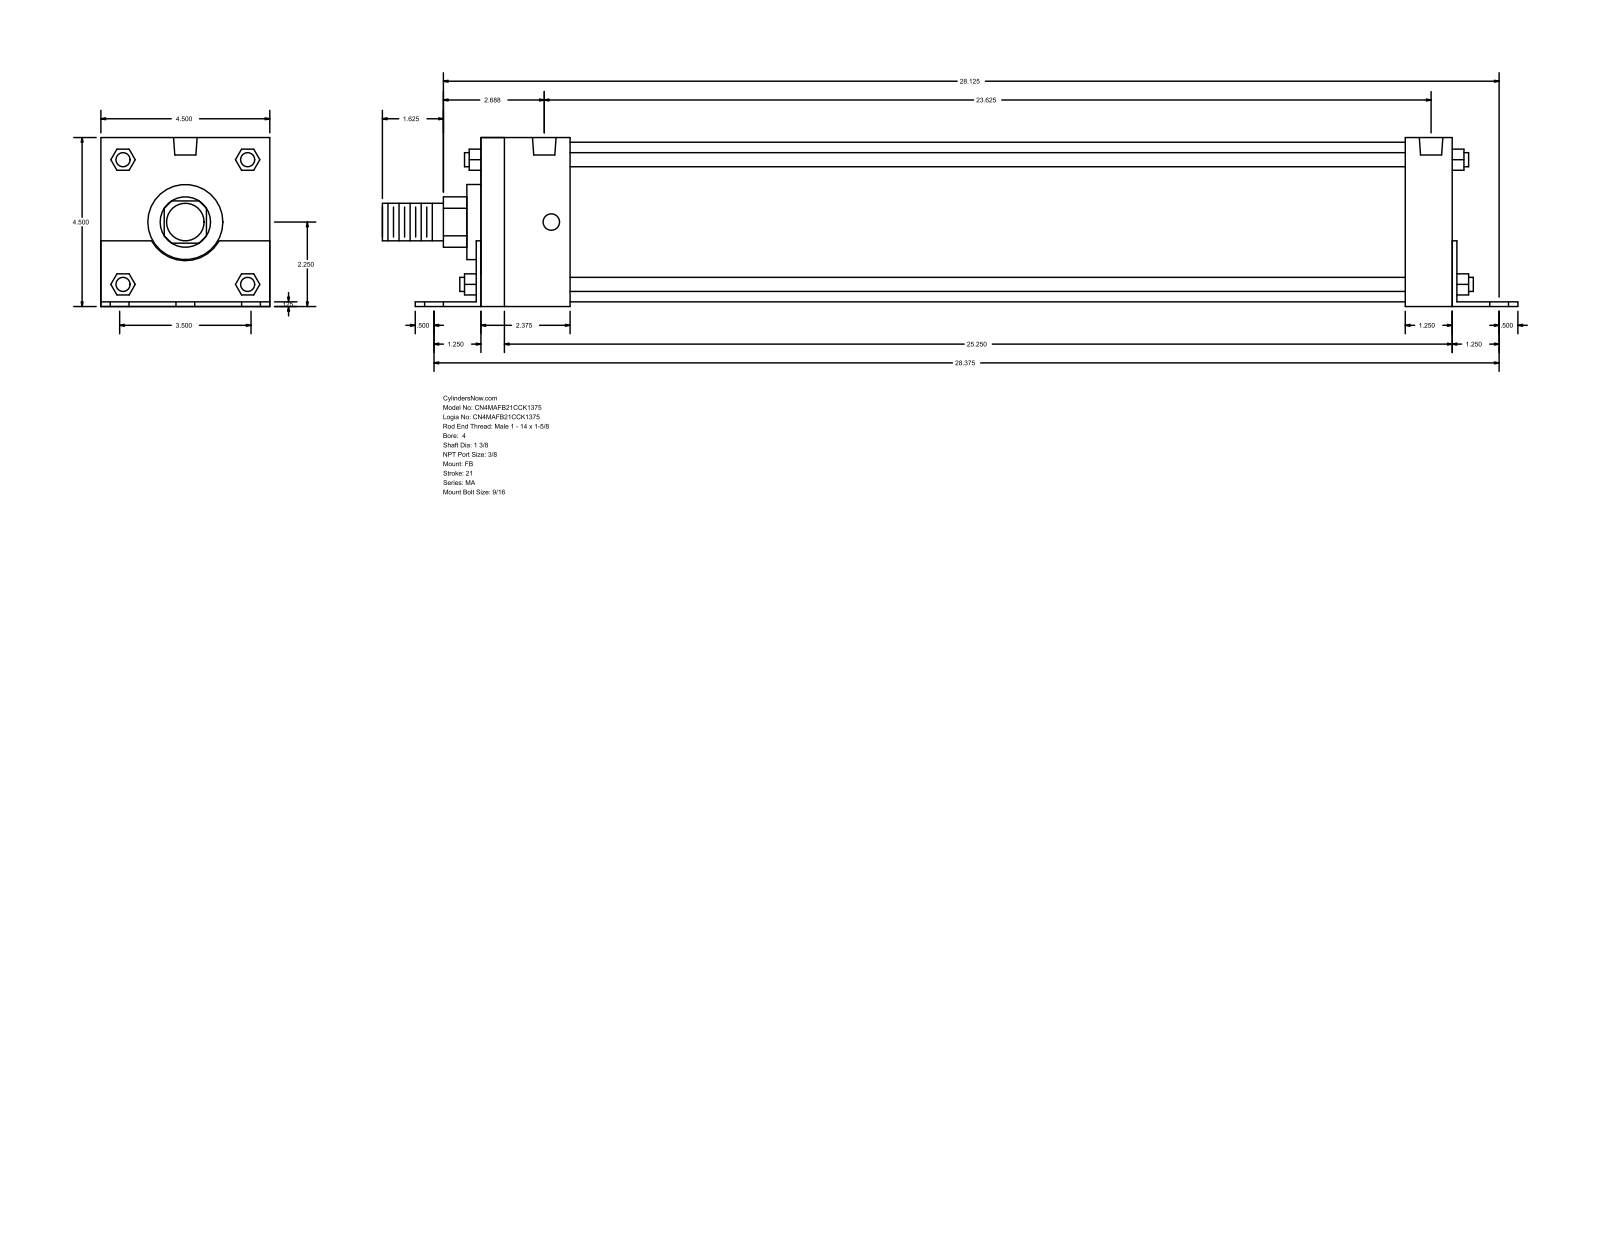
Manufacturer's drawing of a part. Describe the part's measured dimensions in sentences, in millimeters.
The part is named "MA_FB__0400_1.375". Its 3-D file was written by "GSSL Pune (CONFIG_CONTROL_DESIGN)". It is 0 solids with 140 faces: 105 planar, 35 cylindrical and 0 other. Overall it measures 768.35 by 114.35 by 114.3 millimeters. Round holes: 6 of diameter 14.29, 4 of diameter 11.11, 2 of diameter 15.93. Round bosses or shafts: 4 of diameter 9.53, 1 of diameter 107.95, 1 of diameter 50.8, 1 of diameter 34.92, 1 of diameter 25.4. Partial cylindrical surfaces (rounded edges, fillets, slot ends): 1 of radius 17.06, 1 of radius 26.16. The main face-to-face distances are 114.3, 3.17, 114.35, 3.12, 111.18, 657.22, 3.18, 660.4, 660.39, 663.57. The hole center spacings are 44.45, 722.1, 720.73, 64, 67.5, 86.85, 88.9, 90.98.
